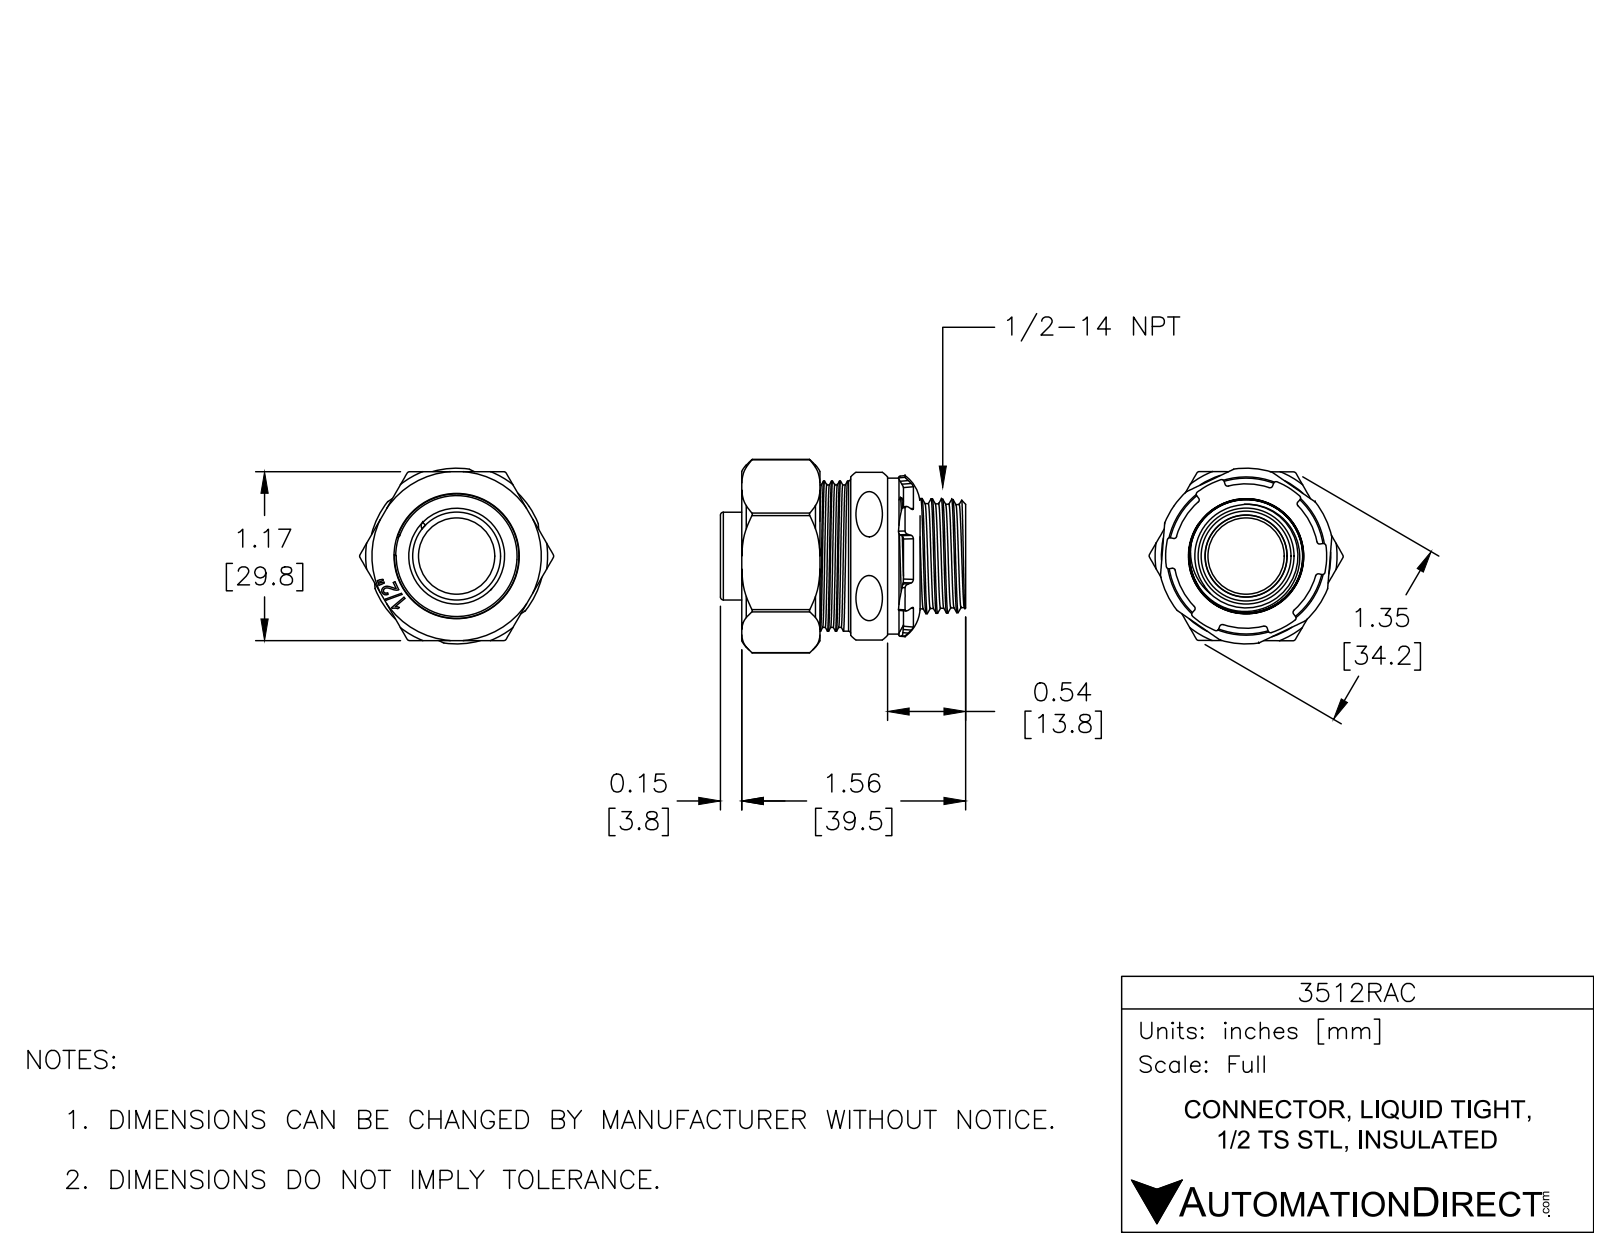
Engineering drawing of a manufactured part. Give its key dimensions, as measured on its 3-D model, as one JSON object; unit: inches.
{"part_name": "3512RAC-2; 3512RAC-4; 3512RAC-8; 3512RAC (+4 more)", "step_written_by": "SolidWorks 2017 (AUTOMOTIVE_DESIGN)", "units": "inches", "bodies": {"solids": 8, "faces": 516, "planar": 197, "cylindrical": 98, "other": 221}, "overall_size": [1.762, 1.344, 1.22], "volume_in3": 0.651, "surface_area_in2": 26.9, "round_holes": [[0.105, 1], [0.529, 1], [0.571, 1], [0.847, 1], [0.858, 1], [0.87, 1], [0.883, 1], [1.016, 1]], "round_bosses_or_shafts": [[1.083, 1], [1.043, 1], [0.992, 1], [0.886, 1], [0.709, 1], [0.61, 1], [0.569, 1], [0.086, 1]], "partial_cylinders_radius": [[0.007, 8], [0.02, 6], [0.034, 2], [0.009, 1], [0.013, 1], [0.025, 1], [0.334, 1]], "face_to_face_distances": [1.013, 1.092, 0.079, 1.173, 1.174, 1.172, 0.933, 0.08, 0.159, 0.543], "hole_center_spacings": [0.5]}
